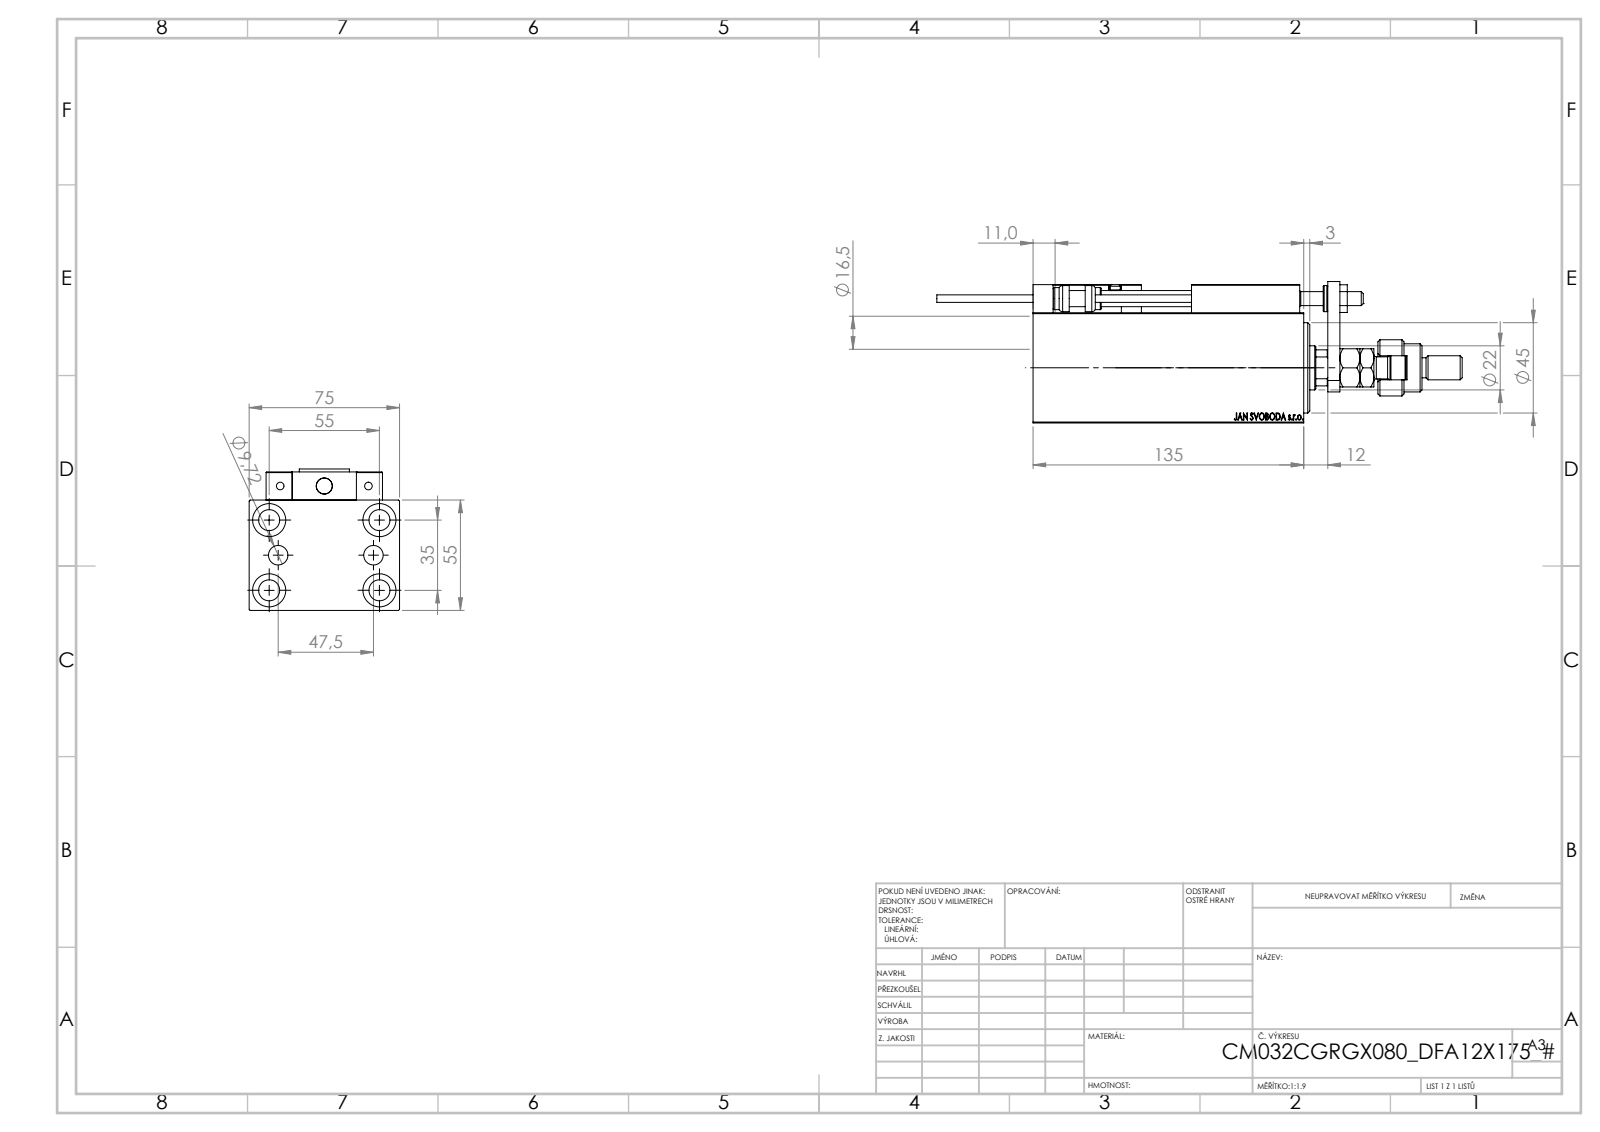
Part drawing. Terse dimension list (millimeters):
name: ALLEN BOLT D5; V450CM_VC_B; SWITCH X; SWITCH_X_FRONT_BACK (+8 more)
written by: SolidWorks 2019 (CONFIG_CONTROL_DESIGN)
unit: mm
bodies: 25 solids, 1363 faces (588 planar, 197 cylindrical, 578 other)
size: 262 × 75 × 70.5
volume: 534 632 mm³; area: 131 029 mm²
holes: 6× ⌀4, 5× ⌀8, 5× ⌀10.5, 5× ⌀16.5, 4× ⌀3.2, 2× ⌀5, 2× ⌀9.72, 1× ⌀7, 1× ⌀22, 1× ⌀25.5, 1× ⌀32, 1× ⌀34
bosses: 2× ⌀11, 2× ⌀5, 2× ⌀3.8, 1× ⌀28, 1× ⌀24, 1× ⌀18, 1× ⌀13, 1× ⌀12
rounds: 30× R0.3, 2× R3, 1× R9.75, 1× R10.5
face distances: 55, 75, 14, 10, 25, 69, 18, 6, 12, 3
hole spacings: 17.9, 32.6, 54.16, 11.37, 20, 23.75, 29.59, 29.69
